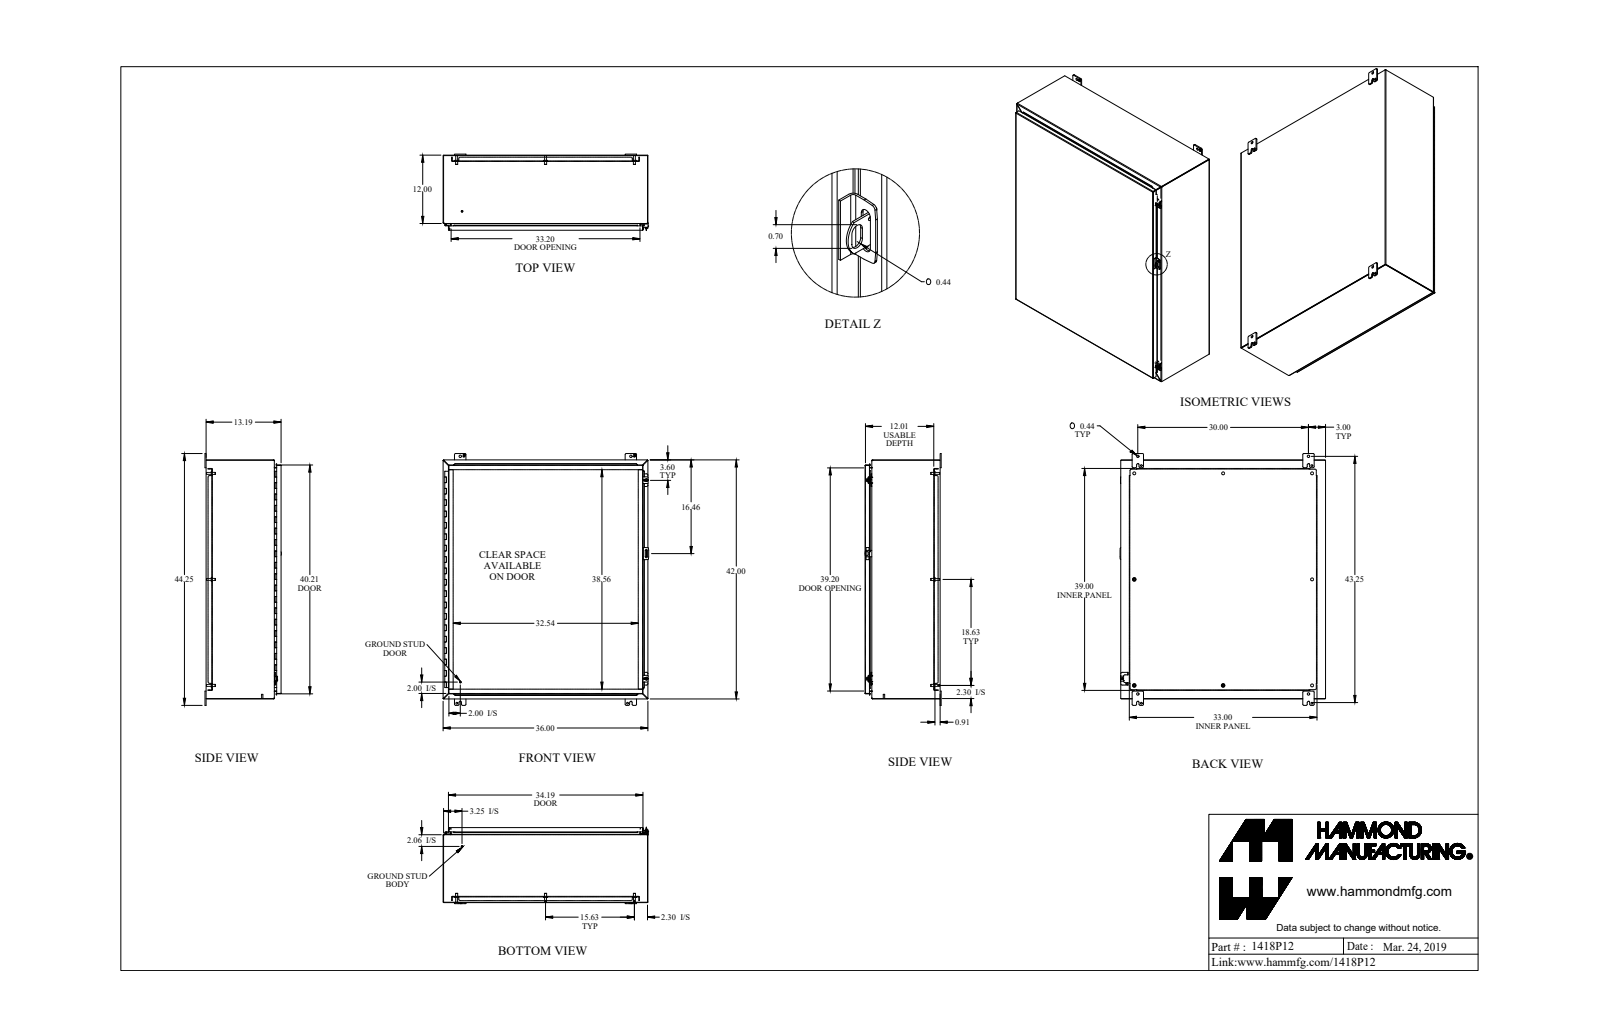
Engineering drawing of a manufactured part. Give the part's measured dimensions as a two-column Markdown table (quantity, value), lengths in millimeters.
| quantity | value |
| --- | --- |
| part name | 1418P12_Default |
| STEP written by | SolidWorks 2019 (CONFIG_CONTROL_DESIGN) |
| units | millimeters |
| bodies | 52 solids, 1548 faces (883 planar, 556 cylindrical, 109 other) |
| overall size | 1124 × 917.6 × 341.3 |
| volume | 9 350 000 mm³ |
| surface area | 9 581 000 mm² |
| round holes (diameter × count) | 12.7 × 8, 7.8 × 4, 8 × 4, 11.1 × 4, 11.3 × 4, 5.4 × 2, 6.7 × 2, 9.5 × 2, 3.2 × 1, 4.7 × 1 |
| round bosses / shafts (diameter × count) | 16.5 × 8, 9.5 × 8, 8.4 × 8, 25.4 × 4, 12.7 × 2, 9.9 × 2, 7.1 × 2, 6.4 × 2 |
| partial cylindrical surfaces (radius × count) | 4.8 × 37, 0.9 × 22, 2.7 × 22, 6.4 × 20, 2.9 × 16, 1.2 × 13, 3.6 × 13, 1 × 8 |
| main face-to-face distances | 1.8, 333.1, 331.2, 334.9, 2.4, 23.8, 25.6, 306.9, 305, 26.2 |
| hole center spacings | 396.9, 473.1, 762, 793.8, 924.1, 946.2, 1026, 44.1 |
